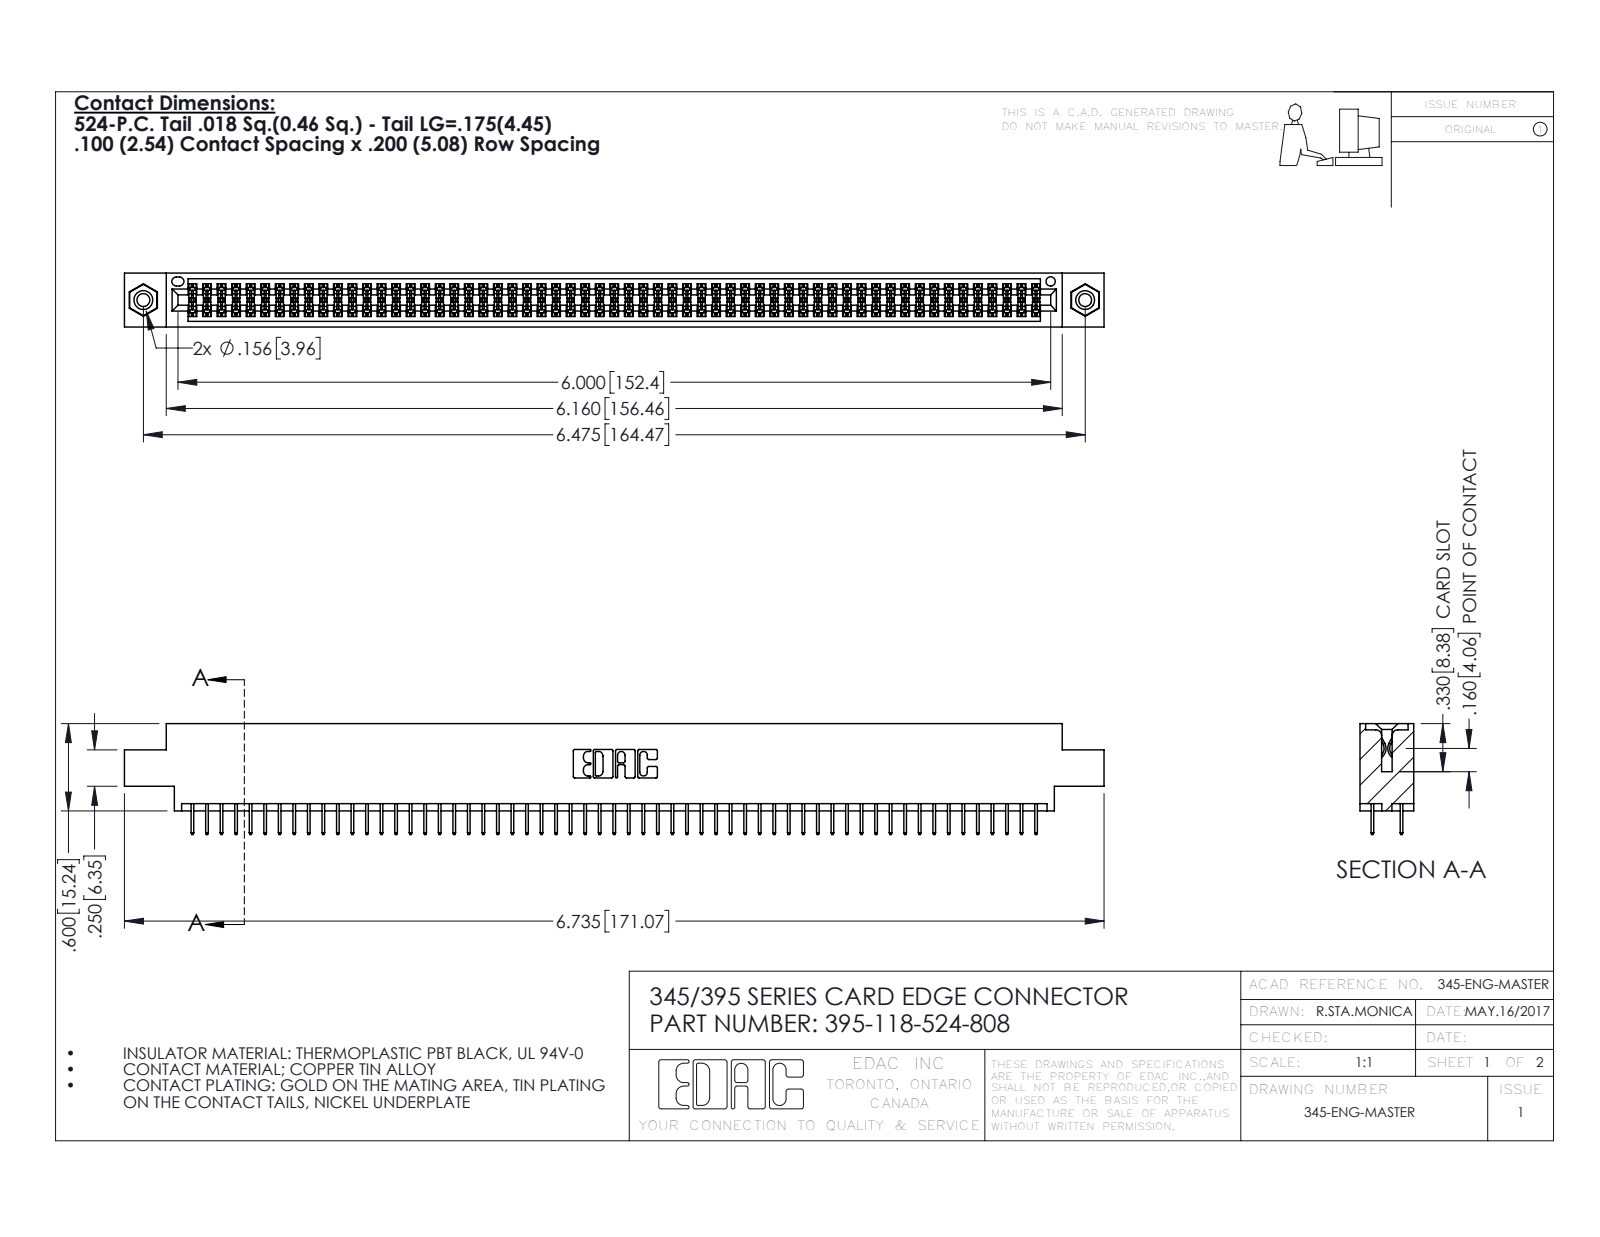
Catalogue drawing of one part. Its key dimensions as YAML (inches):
part_name: "345-292-001_345-293-124; 395-118-524-808; 345-250-001_345-250-003-102; 345 Part_0.170 Offset - 0.156 Dia-TI"
step_written_by: "SolidWorks 2016 (CONFIG_CONTROL_DESIGN)"
units: inches
bodies: {solids: 121, faces: 6562, planar: 4718, cylindrical: 1828, other: 16}
overall_size: [6.735, 0.762, 0.37]
volume: 1.005
surface_area: 37.77
round_holes:
  - {diameter: 0.089, count: 2}
  - {diameter: 0.125, count: 2}
  - {diameter: 0.156, count: 2}
  - {diameter: 0.064, count: 1}
round_bosses_or_shafts:
  - {diameter: 0.155, count: 2}
partial_cylinders:
  - {radius: 0.006, count: 177}
  - {radius: 0.01, count: 22}
  - {radius: 0.007, count: 6}
  - {radius: 0.031, count: 6}
  - {radius: 0.026, count: 3}
  - {radius: 0.014, count: 2}
  - {radius: 0.019, count: 2}
  - {radius: 0.022, count: 2}
face_to_face_distances: [0.072, 0.298, 0.37, 0.2, 0.098, 0.272, 0.025, 0.225, 0.072, 0.175]
hole_center_spacings: [0.27, 6.239, 6.475]
